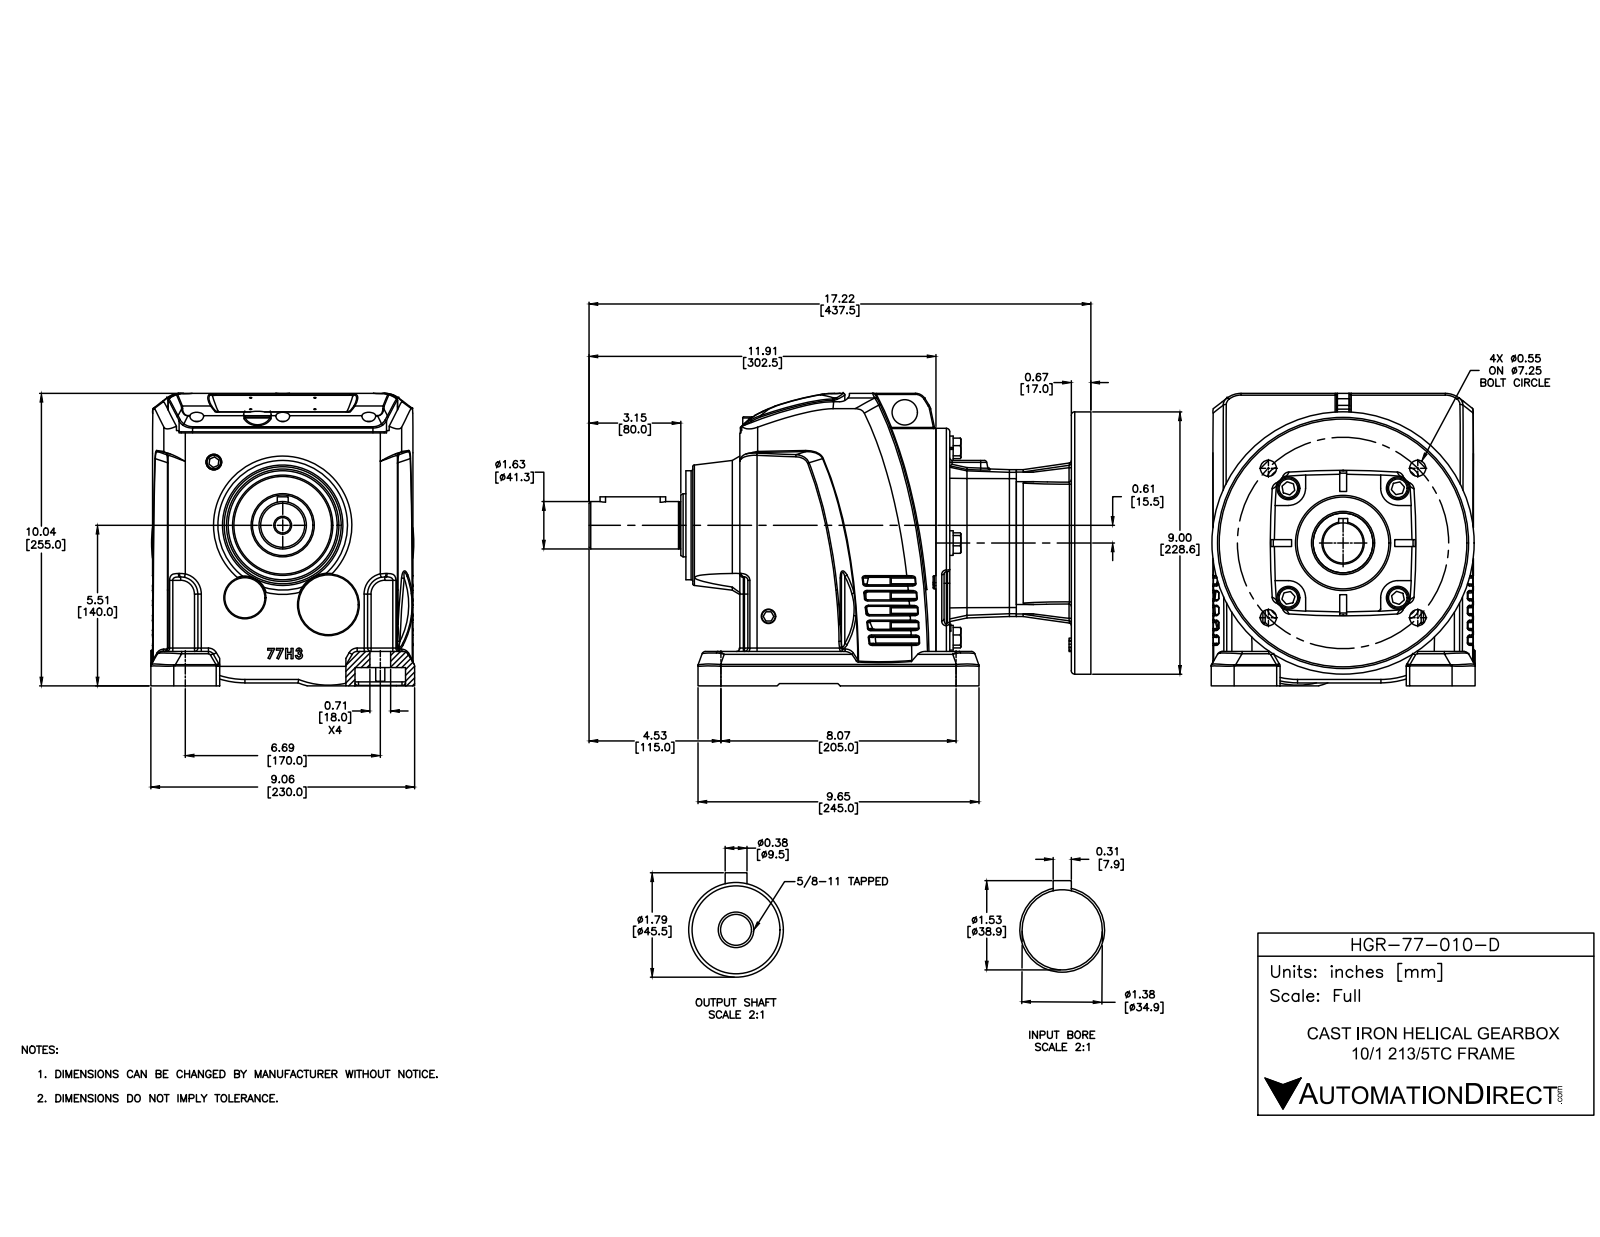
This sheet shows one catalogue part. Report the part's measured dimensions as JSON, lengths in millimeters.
{"part_name": "HGR-77-005-D", "step_written_by": "SolidWorks 2015 (CONFIG_CONTROL_DESIGN)", "units": "millimeters", "bodies": {"solids": 30, "faces": 1264, "planar": 392, "cylindrical": 307, "other": 565}, "overall_size": [437.5, 255, 230], "volume_mm3": 10240000, "surface_area_mm2": 731600, "round_holes": [[12, 6], [2, 4], [14, 4], [18, 4], [20, 4], [55, 2], [13.5, 1], [22, 1], [24, 1], [34.9, 1], [215.9, 1]], "round_bosses_or_shafts": [[13, 5], [21.5, 4], [18, 4], [10, 3], [228.6, 1], [200, 1], [95, 1], [85, 1]], "partial_cylinders_radius": [[3, 42], [1, 33], [2, 11], [15, 8], [12, 6], [5, 4], [6, 4], [8, 4]], "face_to_face_distances": [70, 118, 289, 59.9, 129.9, 300.9, 241, 171, 218, 11.9], "hole_center_spacings": [114.2, 24.6, 67.5, 92.1, 95.5, 130.2, 159.6, 170]}
